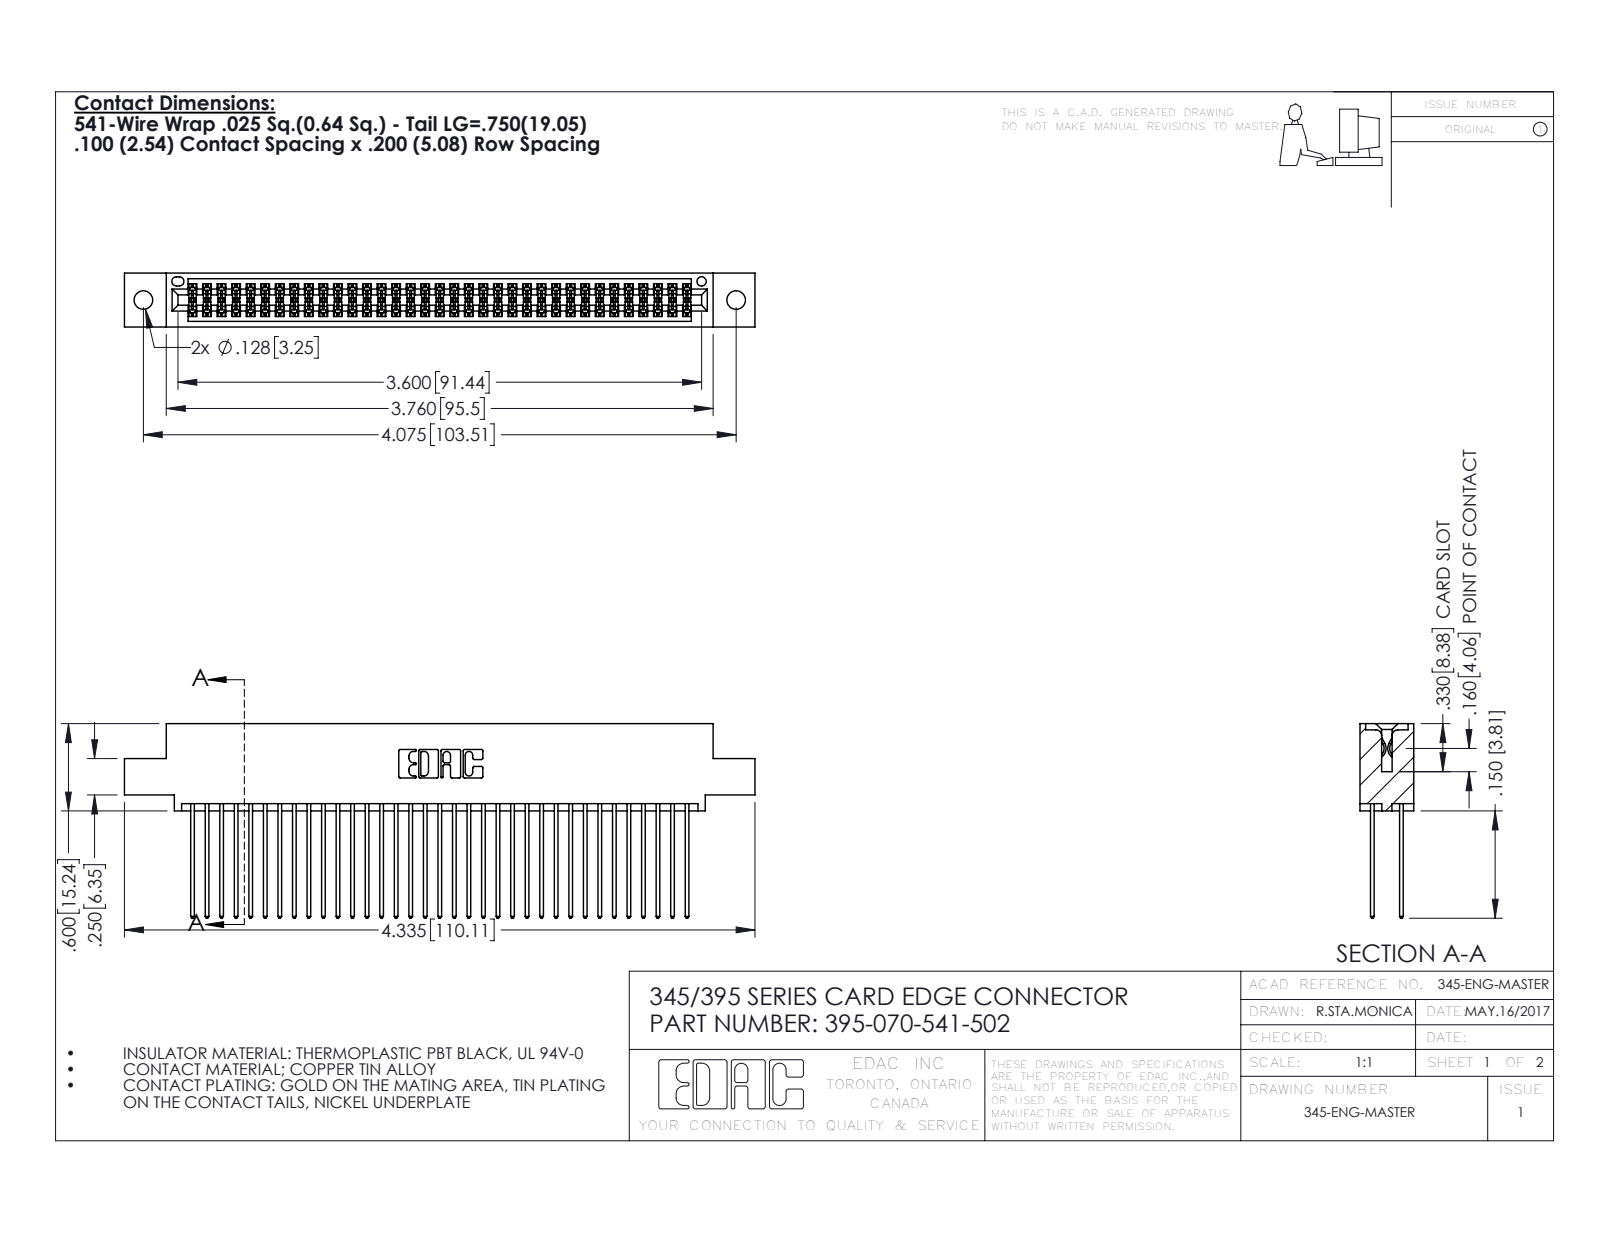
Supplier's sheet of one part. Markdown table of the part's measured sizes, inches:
| quantity | value |
| --- | --- |
| part name | 395-070-541-502; 345-292-001_345-293-141; 345 Part_0.110 Offset - 0.128 Dia |
| STEP written by | SolidWorks 2016 (CONFIG_CONTROL_DESIGN) |
| units | inches |
| bodies | 71 solids, 3630 faces (2394 planar, 1236 cylindrical, 0 other) |
| overall size | 4.335 × 1.337 × 0.37 |
| volume | 0.667 in³ |
| surface area | 27.46 in² |
| round holes (diameter × count) | 0.128 × 2, 0.064 × 1 |
| partial cylindrical surfaces (radius × count) | 0.006 × 105, 0.01 × 70, 0.01 × 22, 0.007 × 6, 0.031 × 6, 0.026 × 3, 0.014 × 2, 0.019 × 2 |
| main face-to-face distances | 0.072, 0.298, 0.2, 0.098, 0.272, 0.025, 0.225, 0.37, 0.175, 0.149 |
| hole center spacings | 0.27, 3.839, 4.075 |
